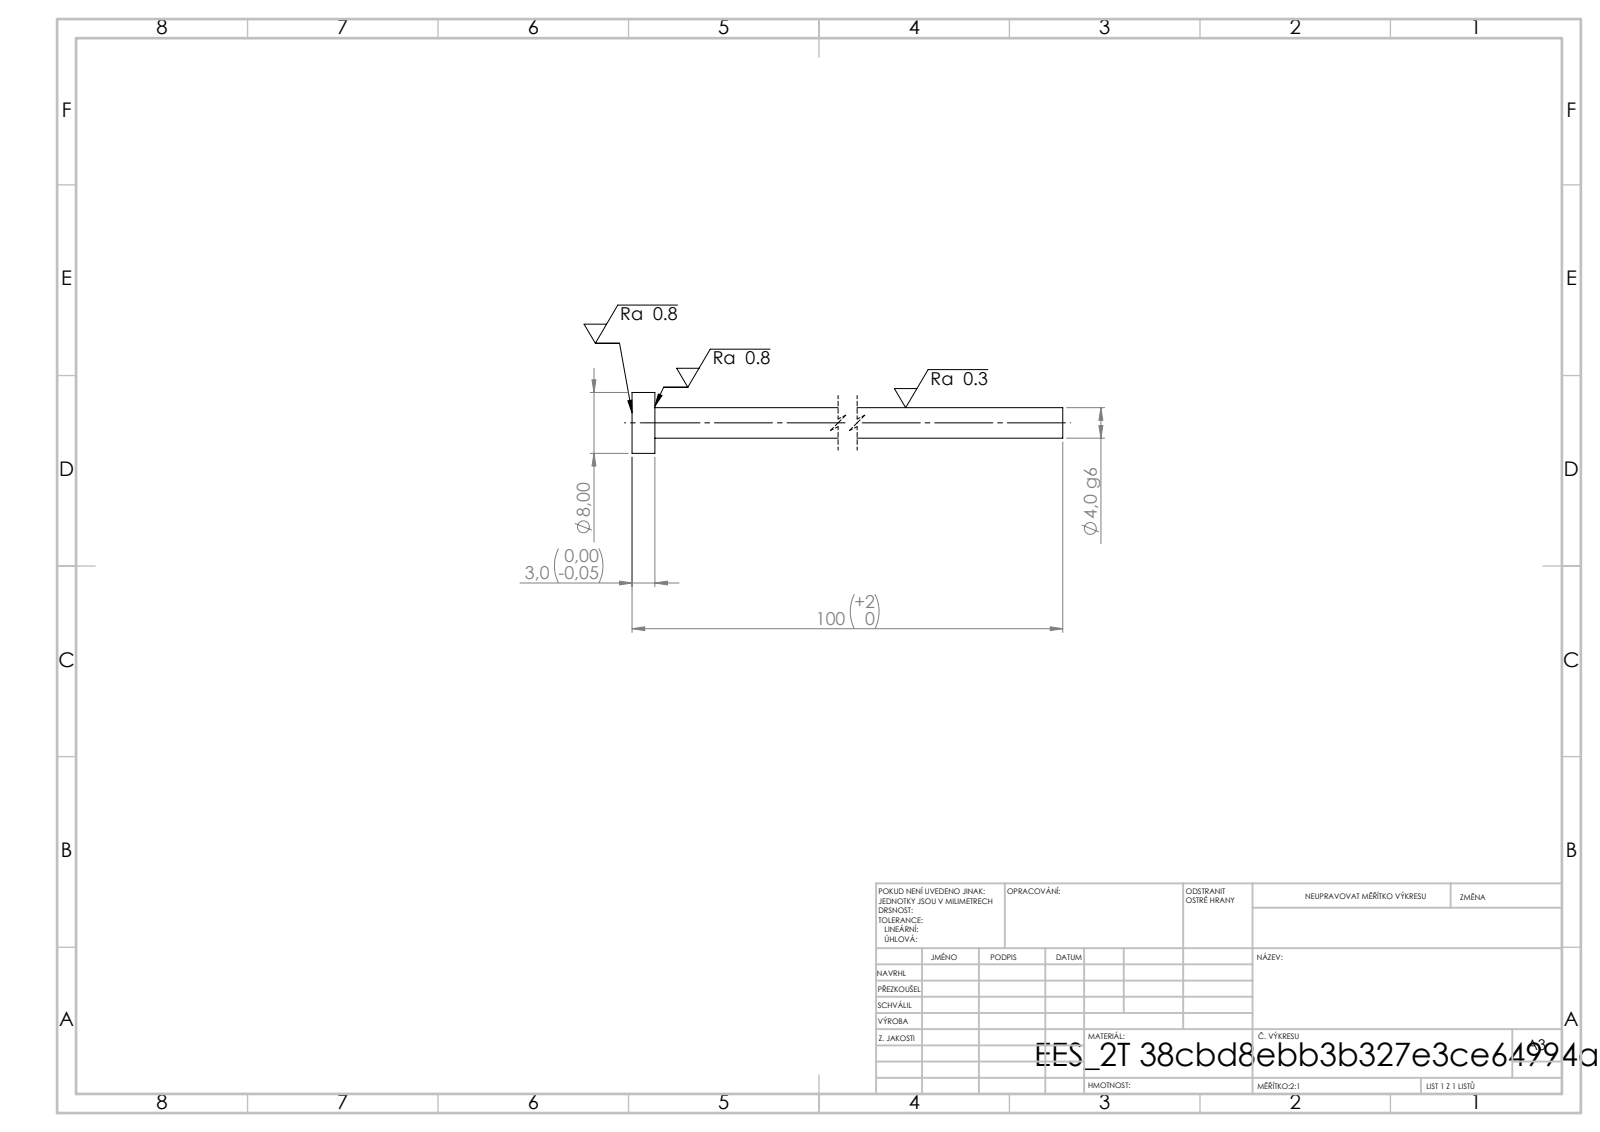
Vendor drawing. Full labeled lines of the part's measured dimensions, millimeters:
STEP written by: SolidWorks 2019 (CONFIG_CONTROL_DESIGN)
Units: millimetres
Bodies: 1 solid, 7 faces (3 planar, 4 cylindrical, 0 other)
Overall size (bounding box): 100 × 8 × 8
Volume: 1 370 mm³ · Surface area: 1 395 mm²
Round bosses / shafts (diameter × count): ⌀8 ×1, ⌀4 ×1
Main face-to-face distances: 3, 100, 97
